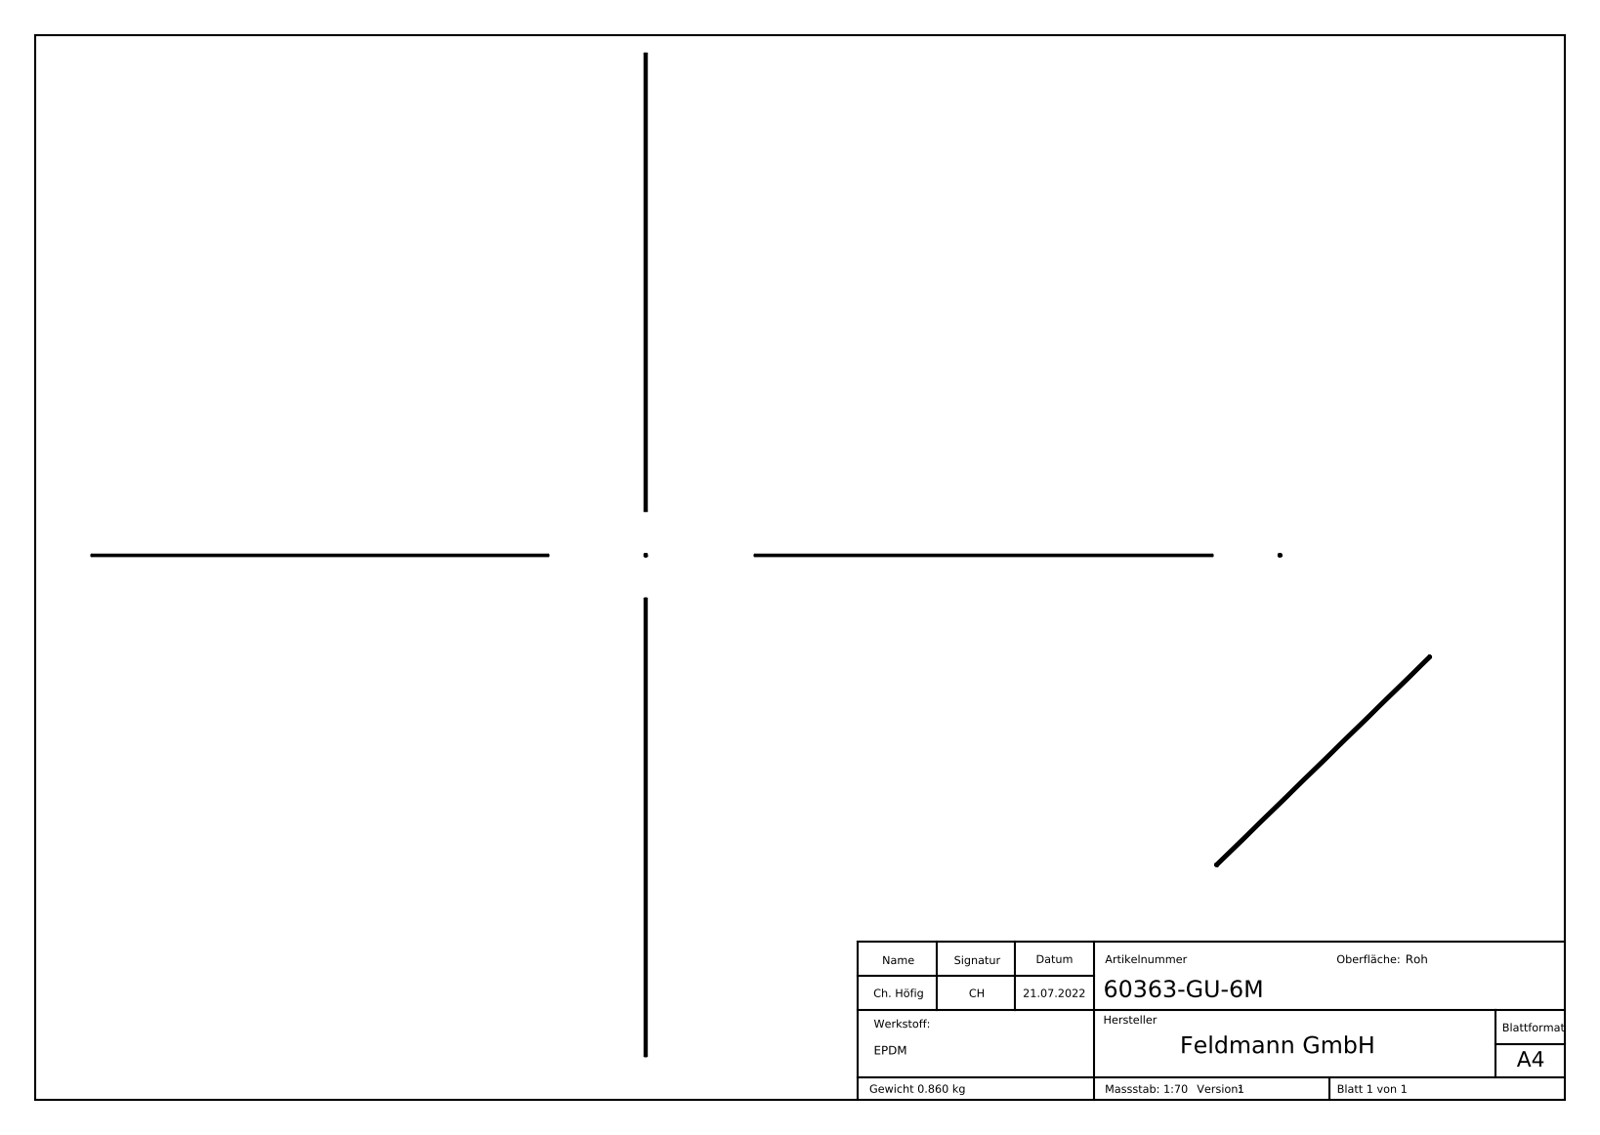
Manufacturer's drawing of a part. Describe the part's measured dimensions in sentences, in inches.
The part is named "60363-GU-6M". Its 3-D file was written by "SolidWorks 2018 (CONFIG_CONTROL_DESIGN)". It is 1 solid with 377 faces: 189 planar, 40 cylindrical and 148 other. Overall it measures 236.22 by 0.992 by 0.906 inches. Its volume is 44.46 cubic inches and its surface area 1 558 square inches. Partial cylindrical surfaces (rounded edges, fillets, slot ends): 22 of radius 0.016, 14 of radius 0.012, 2 of radius 0.039, 2 of radius 0.059. The main face-to-face distances are 0.051, 0.909, 0.059, 0.138, 0.858, 0.961, 0.197, 0.079, 0.061, 0.061.
